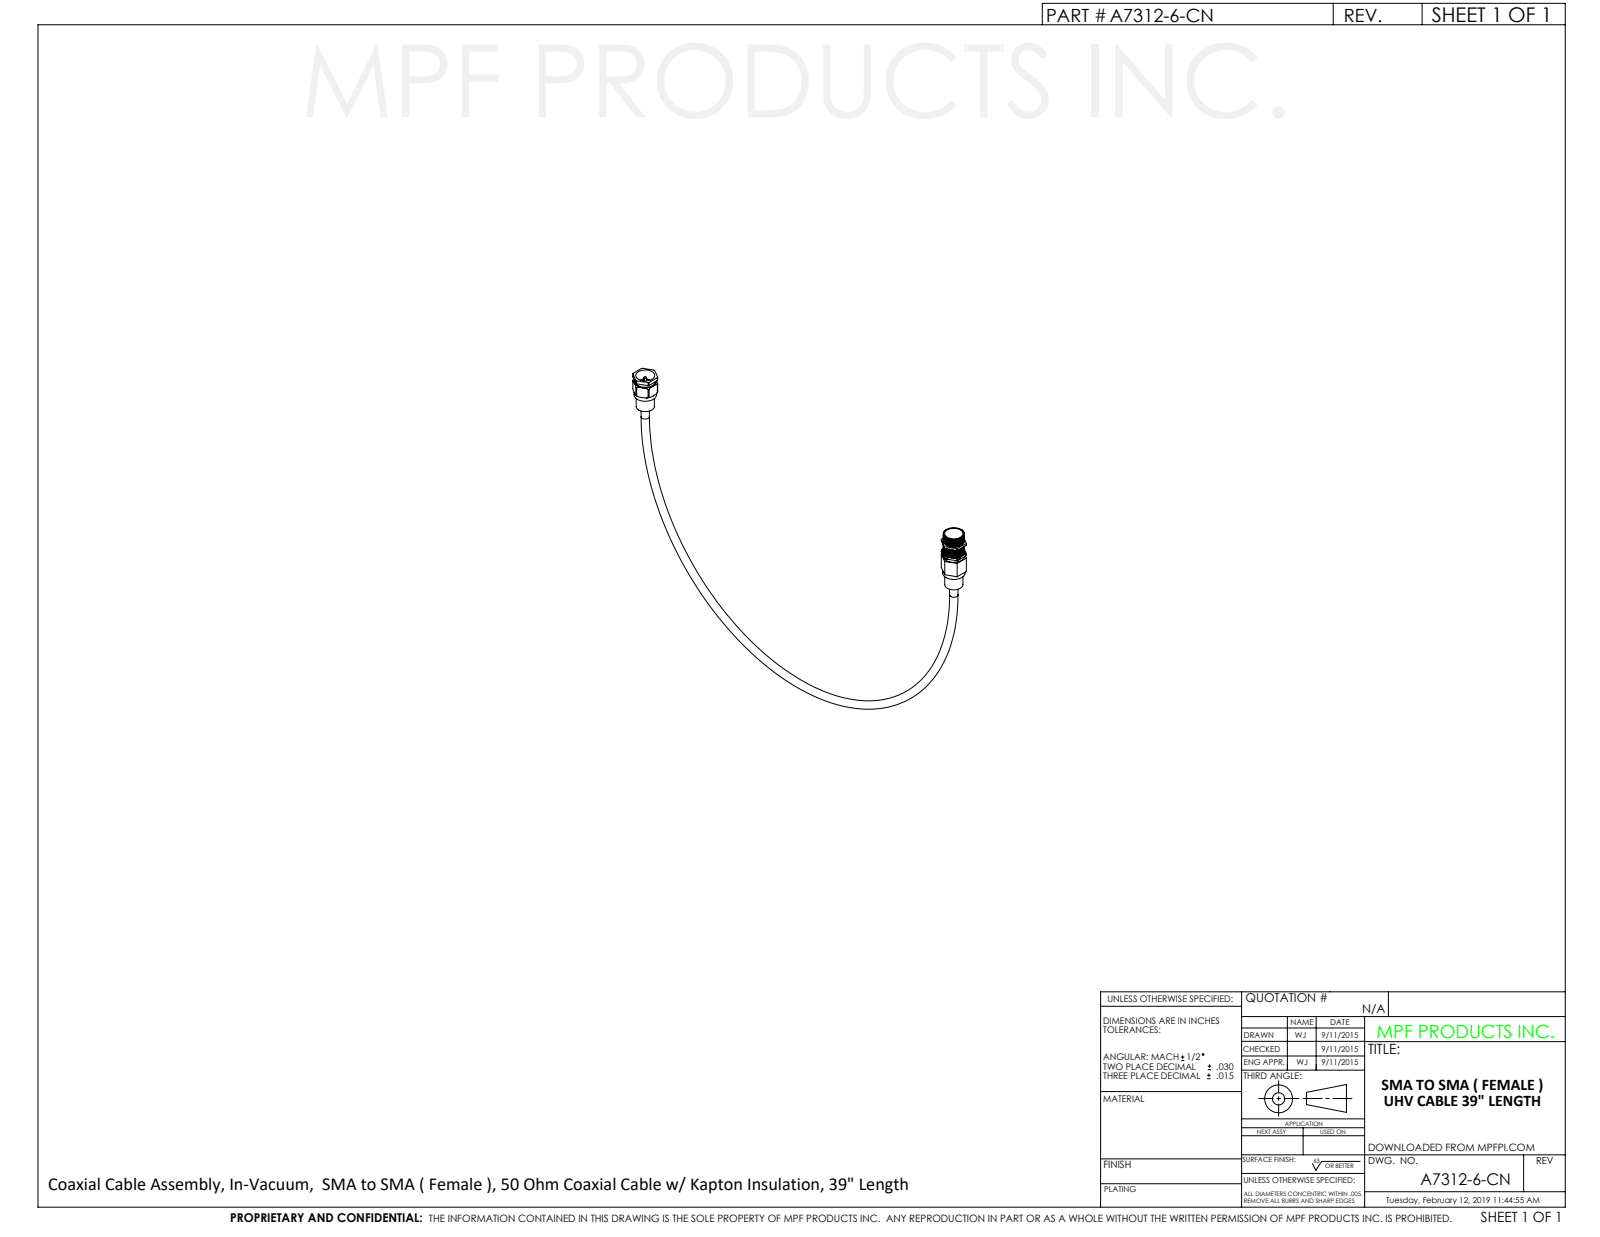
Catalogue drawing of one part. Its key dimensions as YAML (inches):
part_name: "A7311-6-CN"
step_written_by: "SolidWorks 2012 (CONFIG_CONTROL_DESIGN)"
units: inches
bodies: {solids: 5, faces: 265, planar: 87, cylindrical: 84, other: 94}
overall_size: [6.314, 4.089, 0.359]
volume: 0.154
surface_area: 7.338
round_holes:
  - {diameter: 0.05, count: 2}
  - {diameter: 0.115, count: 2}
  - {diameter: 0.167, count: 2}
  - {diameter: 0.186, count: 1}
  - {diameter: 0.251, count: 1}
  - {diameter: 0.257, count: 1}
  - {diameter: 0.26, count: 1}
  - {diameter: 0.292, count: 1}
  - {diameter: 0.293, count: 1}
round_bosses_or_shafts:
  - {diameter: 0.25, count: 2}
  - {diameter: 0.18, count: 2}
  - {diameter: 0.165, count: 2}
  - {diameter: 0.307, count: 1}
  - {diameter: 0.307, count: 1}
  - {diameter: 0.294, count: 1}
  - {diameter: 0.278, count: 1}
  - {diameter: 0.207, count: 1}
partial_cylinders:
  - {radius: 0.175, count: 1}
face_to_face_distances: [0.308, 0.31, 2.691, 2.999, 3.002, 3.309, 0.146, 0.035, 0.274, 0.326]
hole_center_spacings: [6, 6.001]
